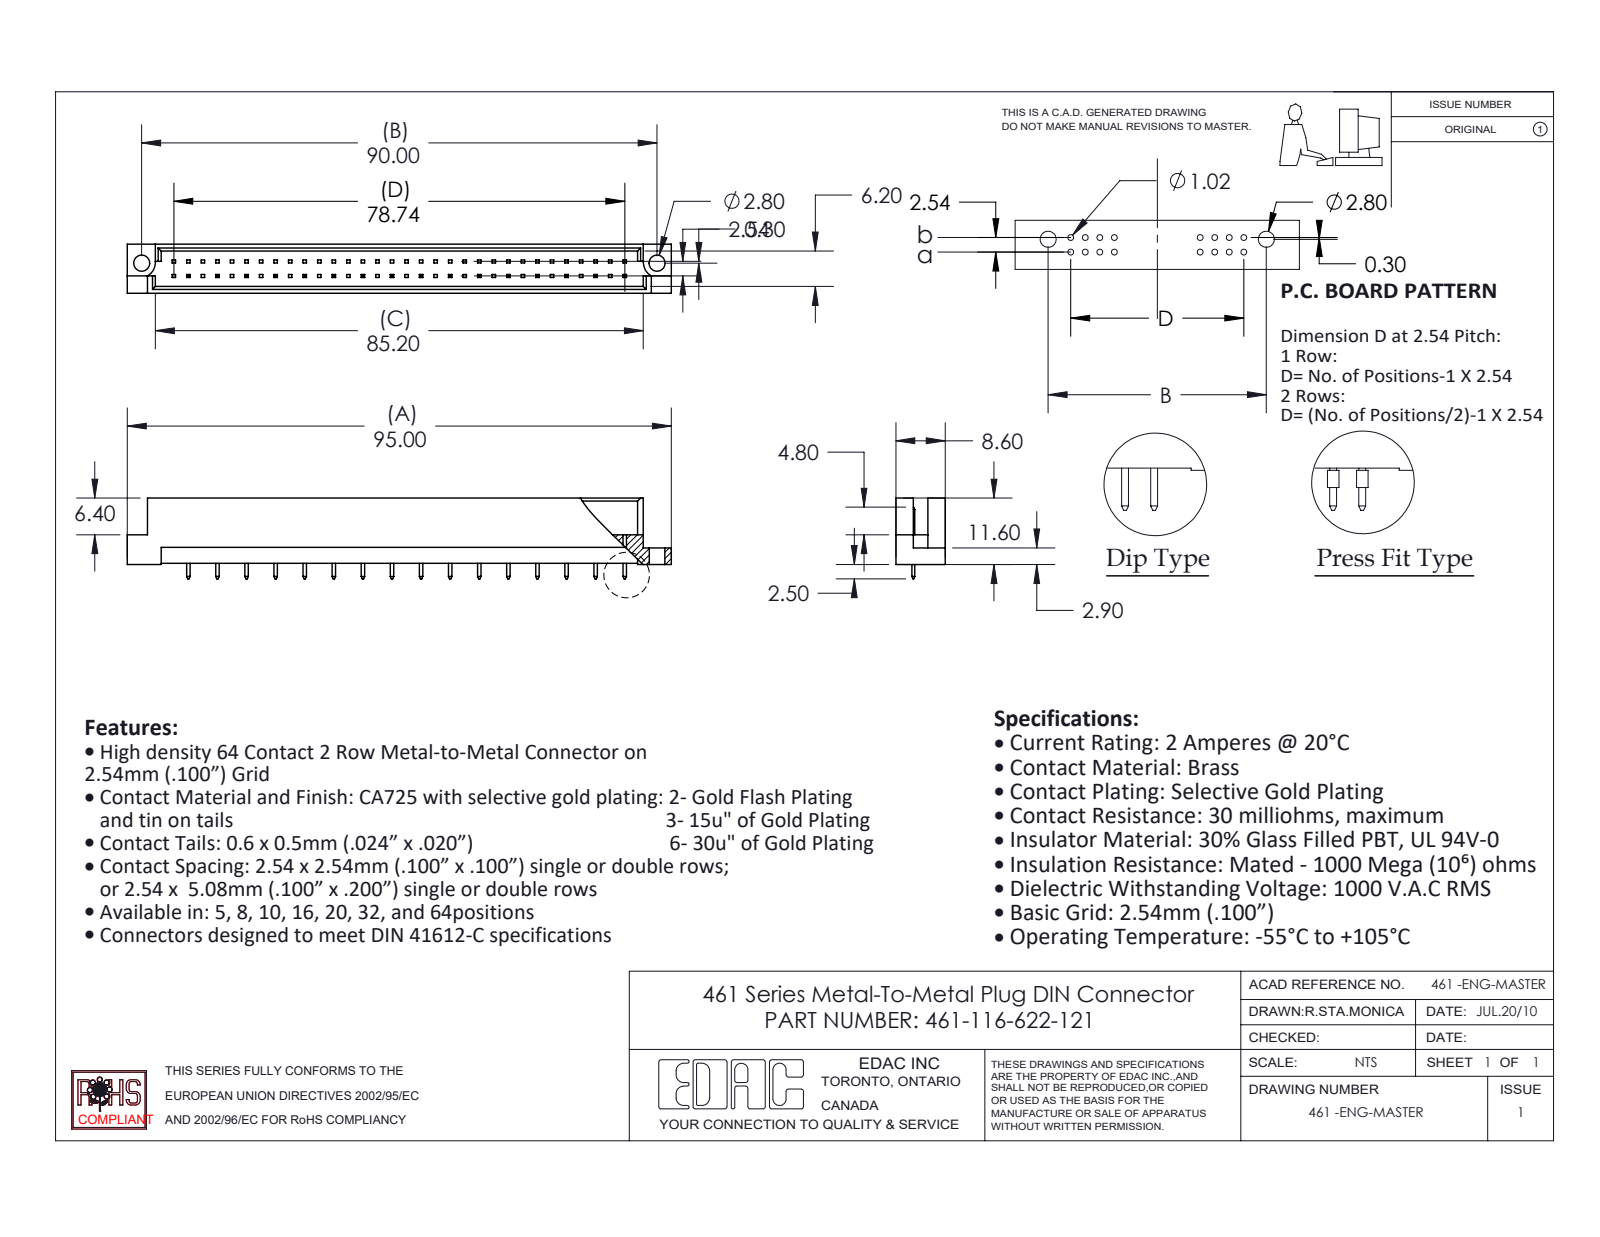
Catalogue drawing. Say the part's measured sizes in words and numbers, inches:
The part is named "461-290_22; 461 Part_64; 461-116-622-121". Its 3-D file was written by "SolidWorks 2020 (CONFIG_CONTROL_DESIGN)". It is 17 solids with 529 faces: 522 planar, 7 cylindrical and 0 other. Overall it measures 3.74 by 0.555 by 0.339 inches. Its volume is 0.288 cubic inches and its surface area 9.464 square inches. Round holes: 2 of diameter 0.11. Partial cylindrical surfaces (rounded edges, fillets, slot ends): 2 of radius 0.11. The main face-to-face distances are 0.047, 0.291, 0.339, 0.244, 0.197, 0.129, 0.209, 0.082, 0.162, 0.109. The hole center spacings are 3.543.
